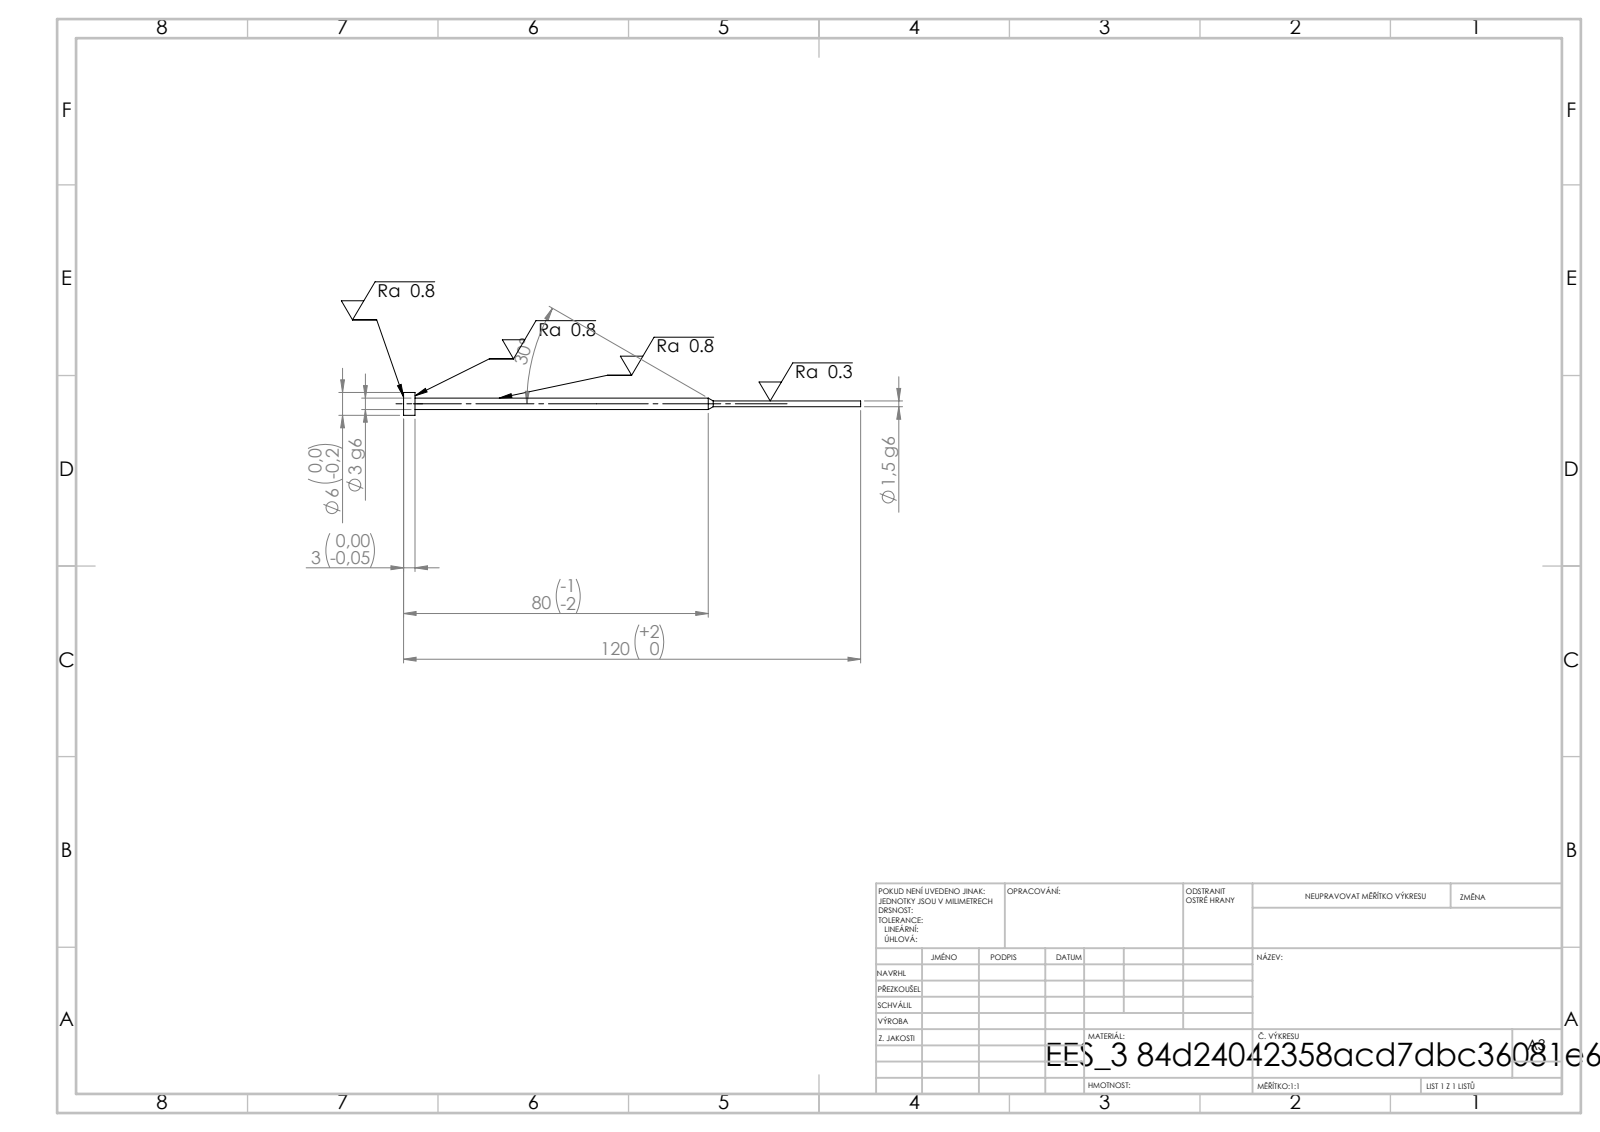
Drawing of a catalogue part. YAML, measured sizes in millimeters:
step_written_by: "SolidWorks 2019 (CONFIG_CONTROL_DESIGN)"
units: millimeters
bodies: {solids: 1, faces: 11, planar: 3, cylindrical: 6, other: 2}
overall_size: [120, 6, 6]
volume: 703
surface_area: 1026
round_bosses_or_shafts:
  - {diameter: 6, count: 1}
  - {diameter: 3, count: 1}
  - {diameter: 1.5, count: 1}
face_to_face_distances: [3, 117, 120]
